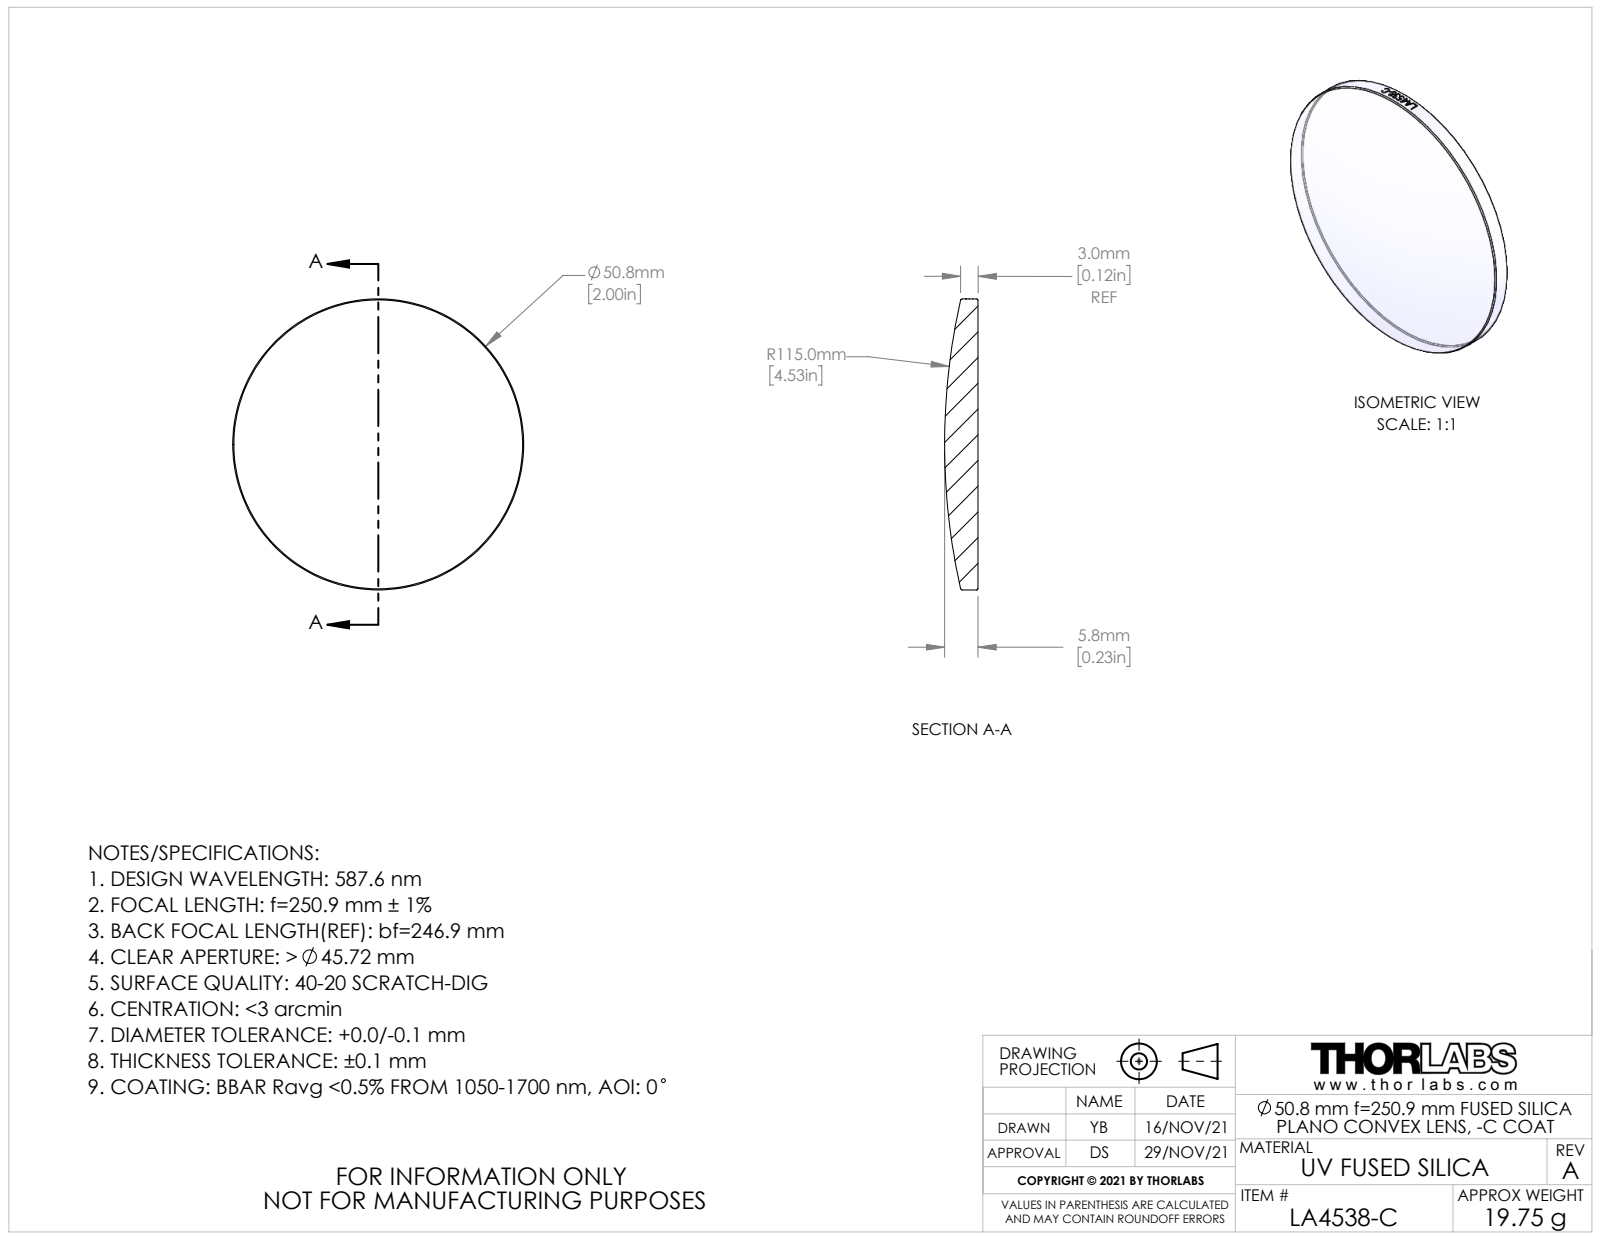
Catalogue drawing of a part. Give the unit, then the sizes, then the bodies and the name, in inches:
Units: inches
Overall size (bounding box): 2 × 2 × 0.23
Round bosses / shafts (diameter × count): ⌀2 ×1
Volume: 0.547 in³ · Surface area: 7.014 in²
Bodies: 1 solid, 21 faces (1 planar, 14 cylindrical, 6 other)
Part name (STEP PRODUCT): CTN018077-E0W; CTN018146
STEP written by: SolidWorks 2018 (AUTOMOTIVE_DESIGN)
